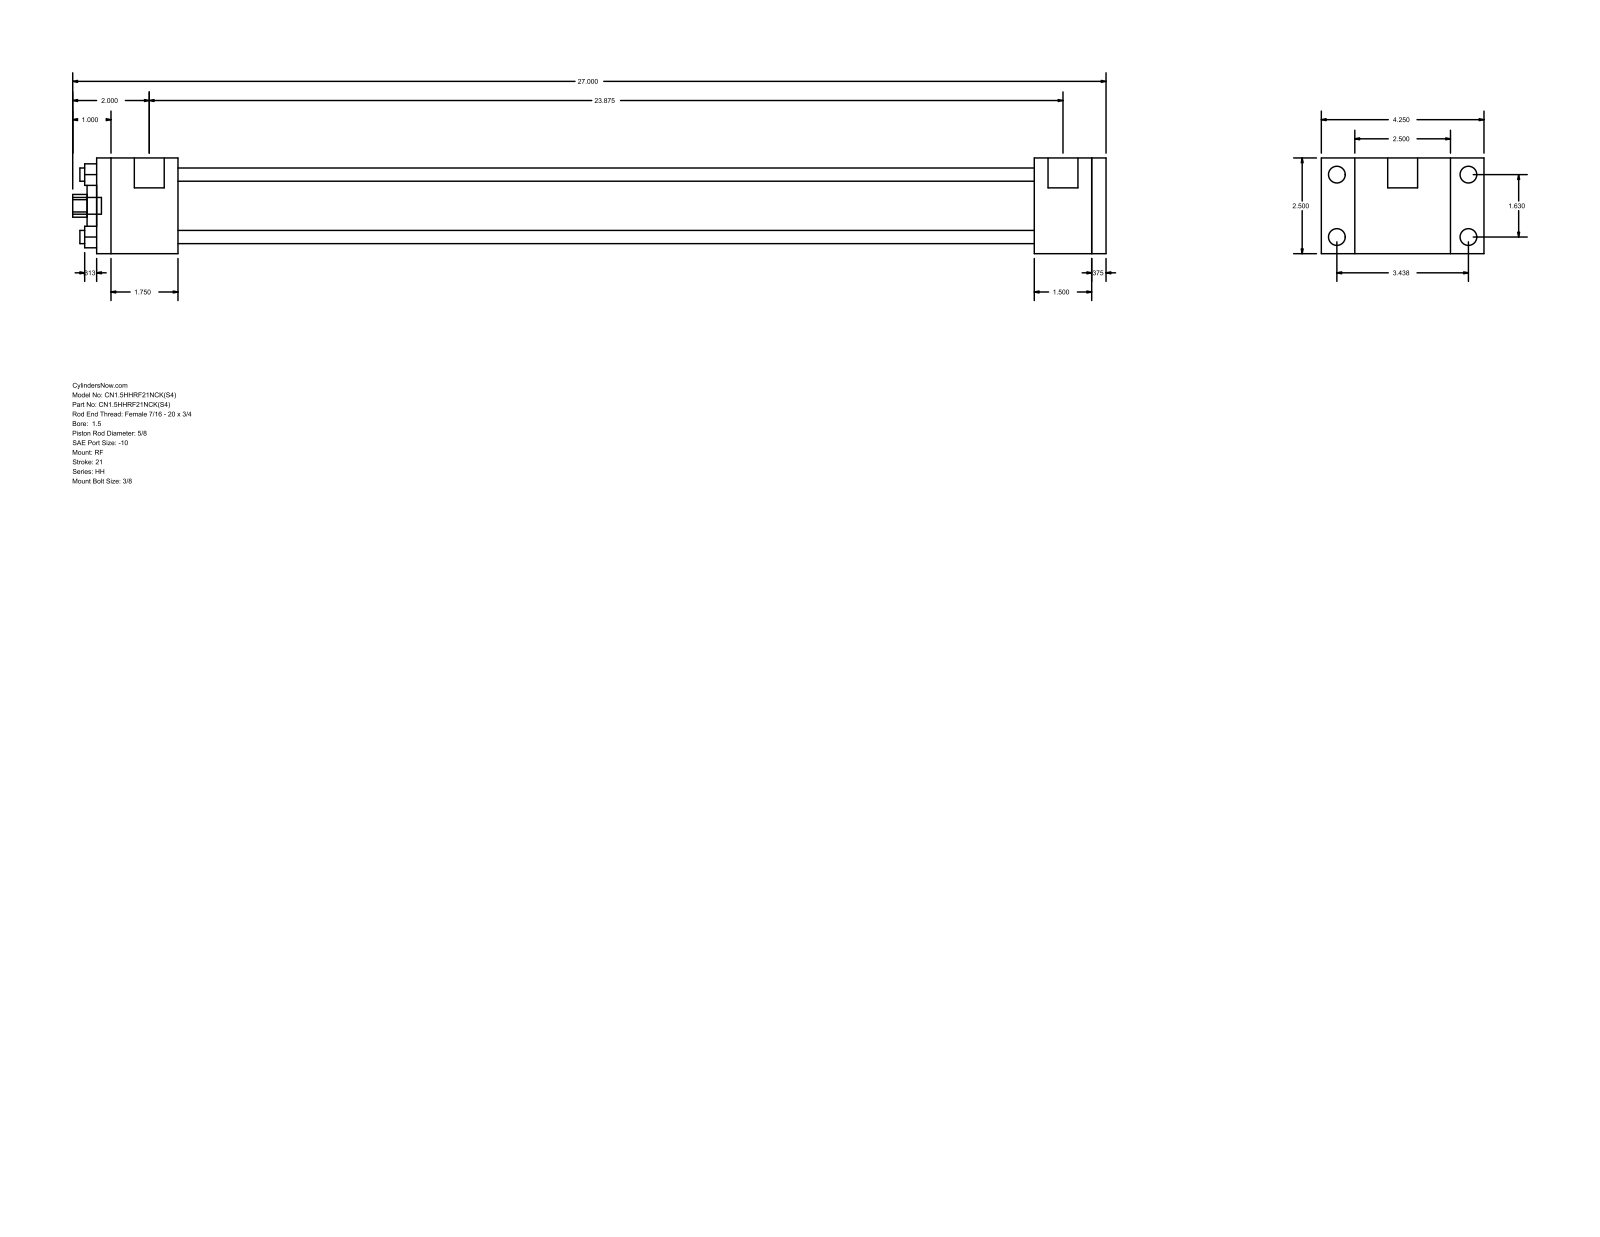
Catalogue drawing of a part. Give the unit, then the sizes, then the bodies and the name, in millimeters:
Units: millimetres
Overall size (bounding box): 685.8 × 107.95 × 63.5
Round holes (diameter × count): ⌀8.76 ×4, ⌀15.88 ×1, ⌀28.57 ×1, ⌀44.45 ×1
Round bosses / shafts (diameter × count): ⌀11.13 ×4, ⌀5.56 ×4, ⌀19.84 ×2, ⌀11.11 ×1
Partial cylindrical surfaces — rounded edges, fillets, slot ends (radius × count): R7.54 ×1
Main face-to-face distances: 63.5, 669.92, 9.53, 38.1, 660.39, 47.63, 53.97, 622.29, 568.32, 606.42
Hole centre spacings: 29.27, 41.4, 58.55
Bodies: 0 solids, 92 faces (64 planar, 28 cylindrical, 0 other)
Part name (STEP PRODUCT): HH_RF__0150_0.625
STEP written by: GSSL Pune (CONFIG_CONTROL_DESIGN)
